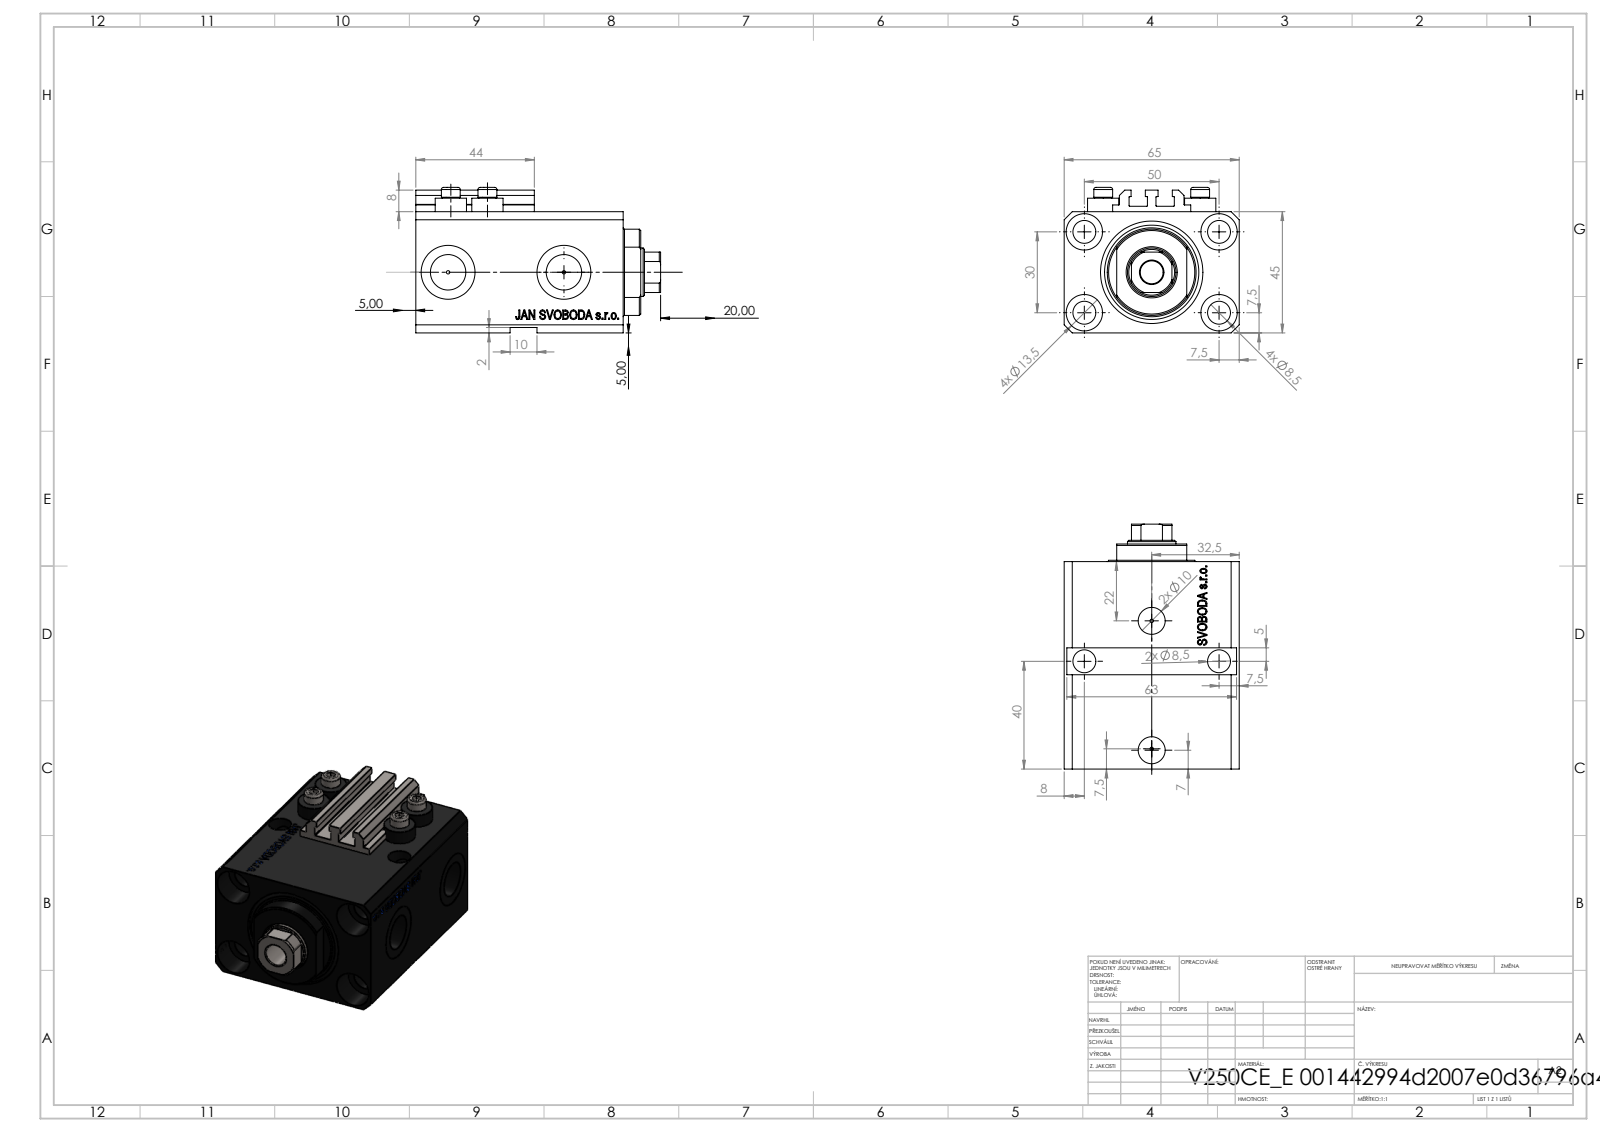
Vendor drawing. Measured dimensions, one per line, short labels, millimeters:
name: V250CE_E_Body; V250CE_VC_E; ALLEN BOLT V250CE; V250CE_C_VCP
written by: SolidWorks 2019 (CONFIG_CONTROL_DESIGN)
unit: mm
bodies: 8 solids, 1083 faces (515 planar, 138 cylindrical, 430 other)
size: 91 × 65 × 54
volume: 196 158 mm³; area: 60 322 mm²
holes: 7× ⌀8.5, 4× ⌀1.25, 4× ⌀4, 4× ⌀13.5, 2× ⌀10, 2× ⌀13.16, 2× ⌀20, 1× ⌀18, 1× ⌀25, 1× ⌀38
bosses: 4× ⌀11.6, 4× ⌀7
rounds: 10× R0.2, 1× R8.5, 1× R16
face distances: 45, 65, 63, 14, 77, 2, 6.9, 56.1, 70.1, 47
hole spacings: 29.15, 50, 13.6, 15.12, 18.81, 18.97, 26.22, 26.61
